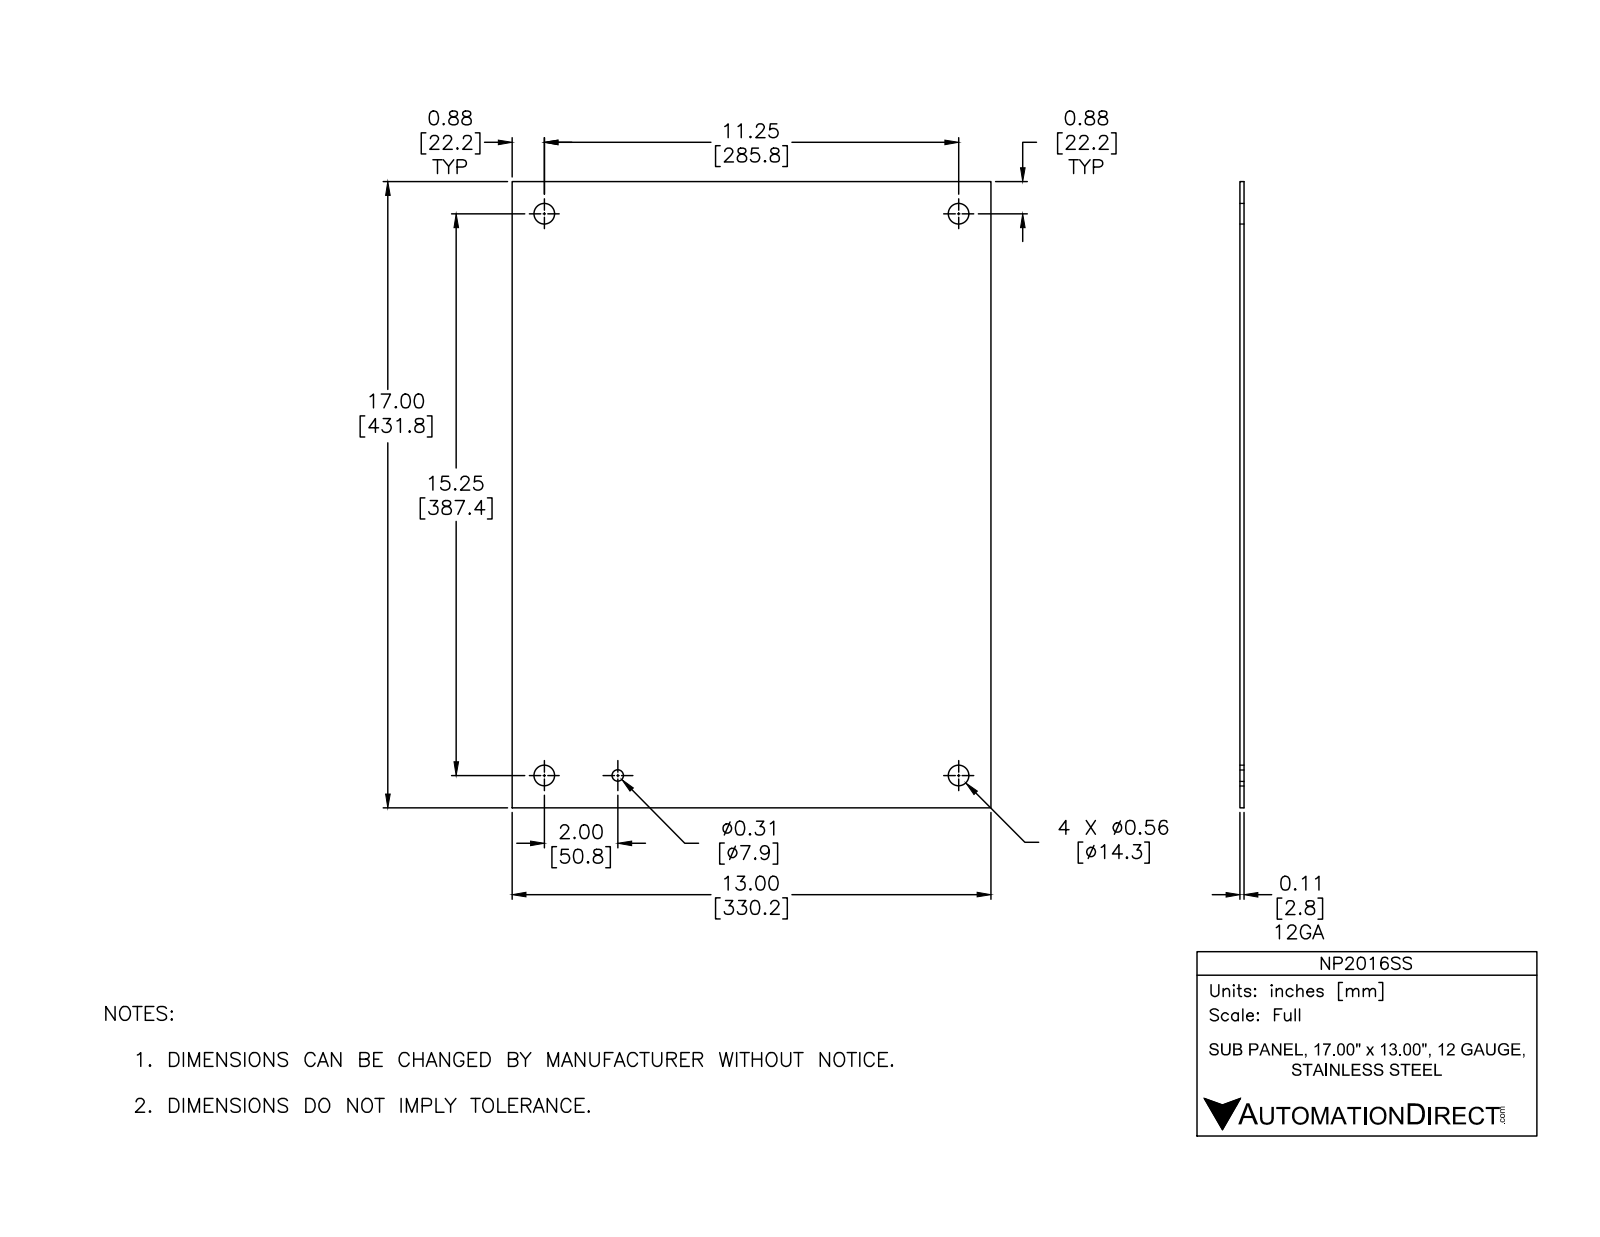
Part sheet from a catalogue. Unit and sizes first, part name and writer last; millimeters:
Units: millimetres
Overall size (bounding box): 431.8 × 330.2 × 2.4
Round holes (diameter × count): ⌀14.3 ×4, ⌀7.9 ×1
Main face-to-face distances: 2.4, 330.2, 431.8
Hole centre spacings: 285.8, 50.8, 235, 387.4, 387.4, 390.7, 453, 481.4
Volume: 337 700 mm³ · Surface area: 287 900 mm²
Bodies: 1 solid, 11 faces (6 planar, 5 cylindrical, 0 other)
Part name (STEP PRODUCT): NP2016SS
STEP written by: Autodesk Inventor 2012 (AUTOMOTIVE_DESIGN)
